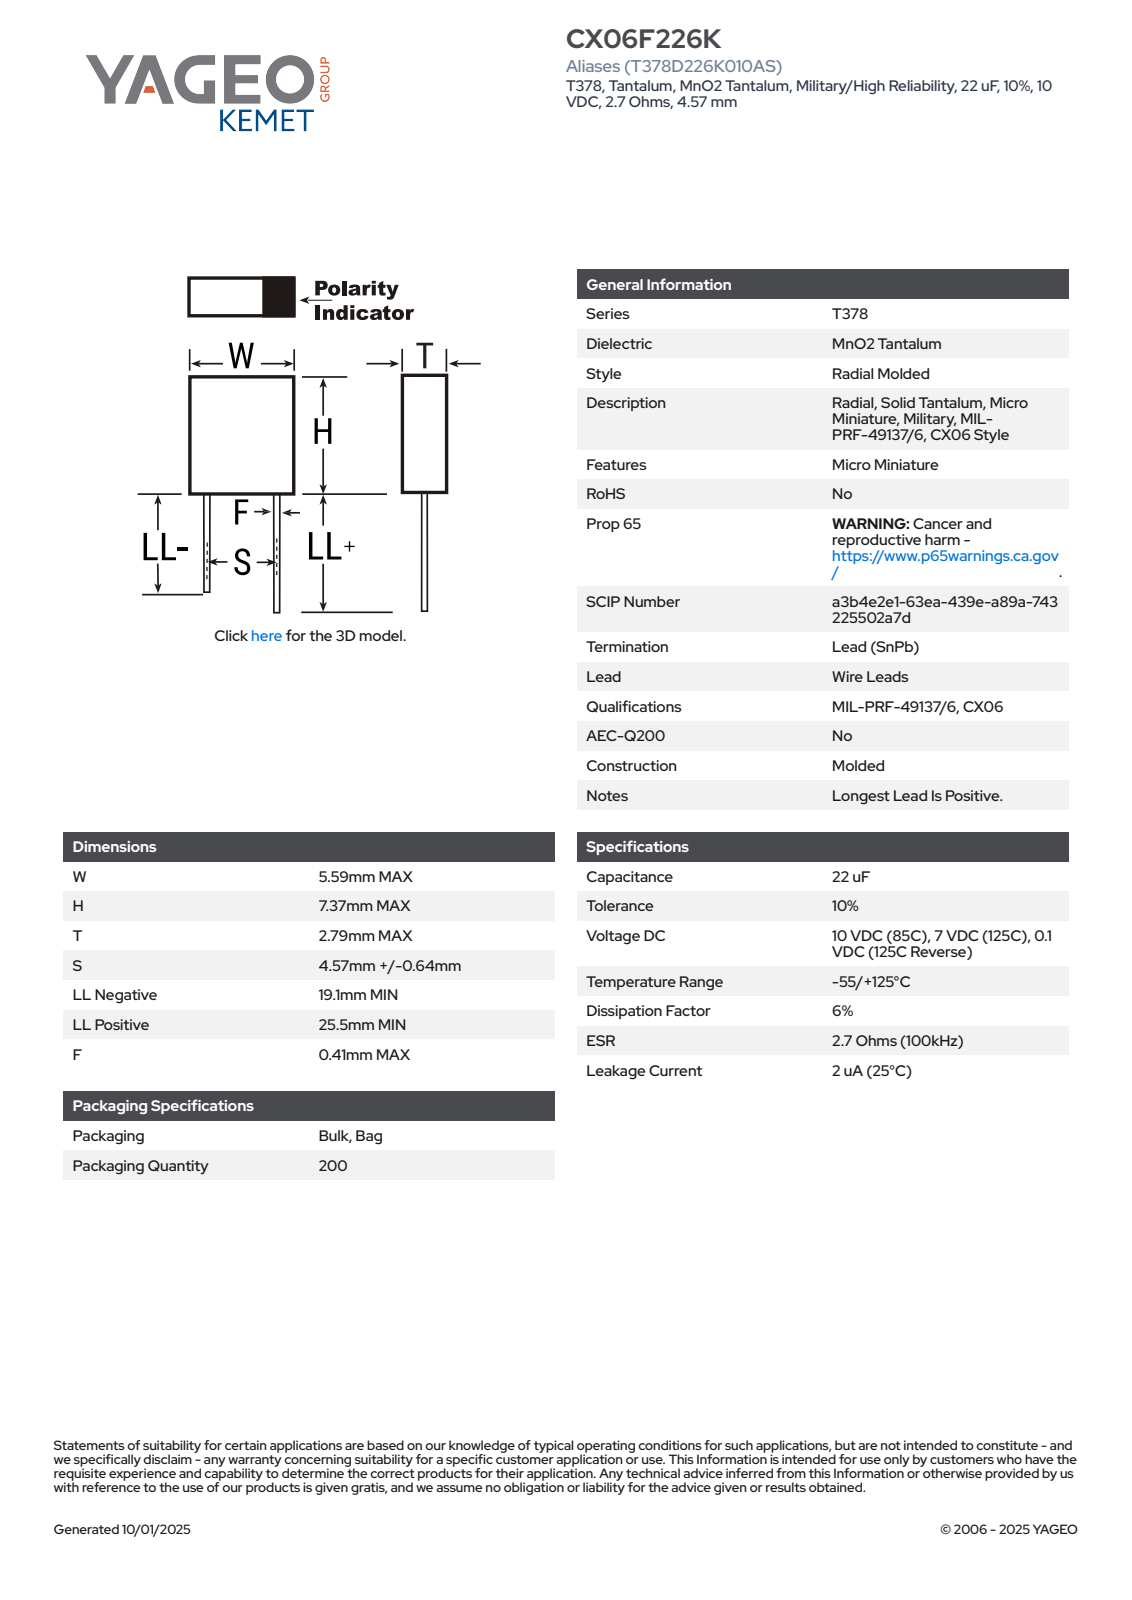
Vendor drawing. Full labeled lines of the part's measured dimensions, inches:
Part name (STEP PRODUCT): CTRM_T378_W5.59H7.37T2.79S4.57LL44.46F0.44
STEP written by: SolidWorks 2014 (AUTOMOTIVE_DESIGN)
Units: inches
Bodies: 4 solids, 71 faces (67 planar, 4 cylindrical, 0 other)
Overall size (bounding box): 2.041 × 0.22 × 0.11
Volume: 0.008 in³ · Surface area: 0.425 in²
Round bosses / shafts (diameter × count): ⌀0.017 ×2
Main face-to-face distances: 0.11, 0.22, 0.29, 1.5, 1.791, 0.25, 1.75, 2.041, 0.163, 0.037
